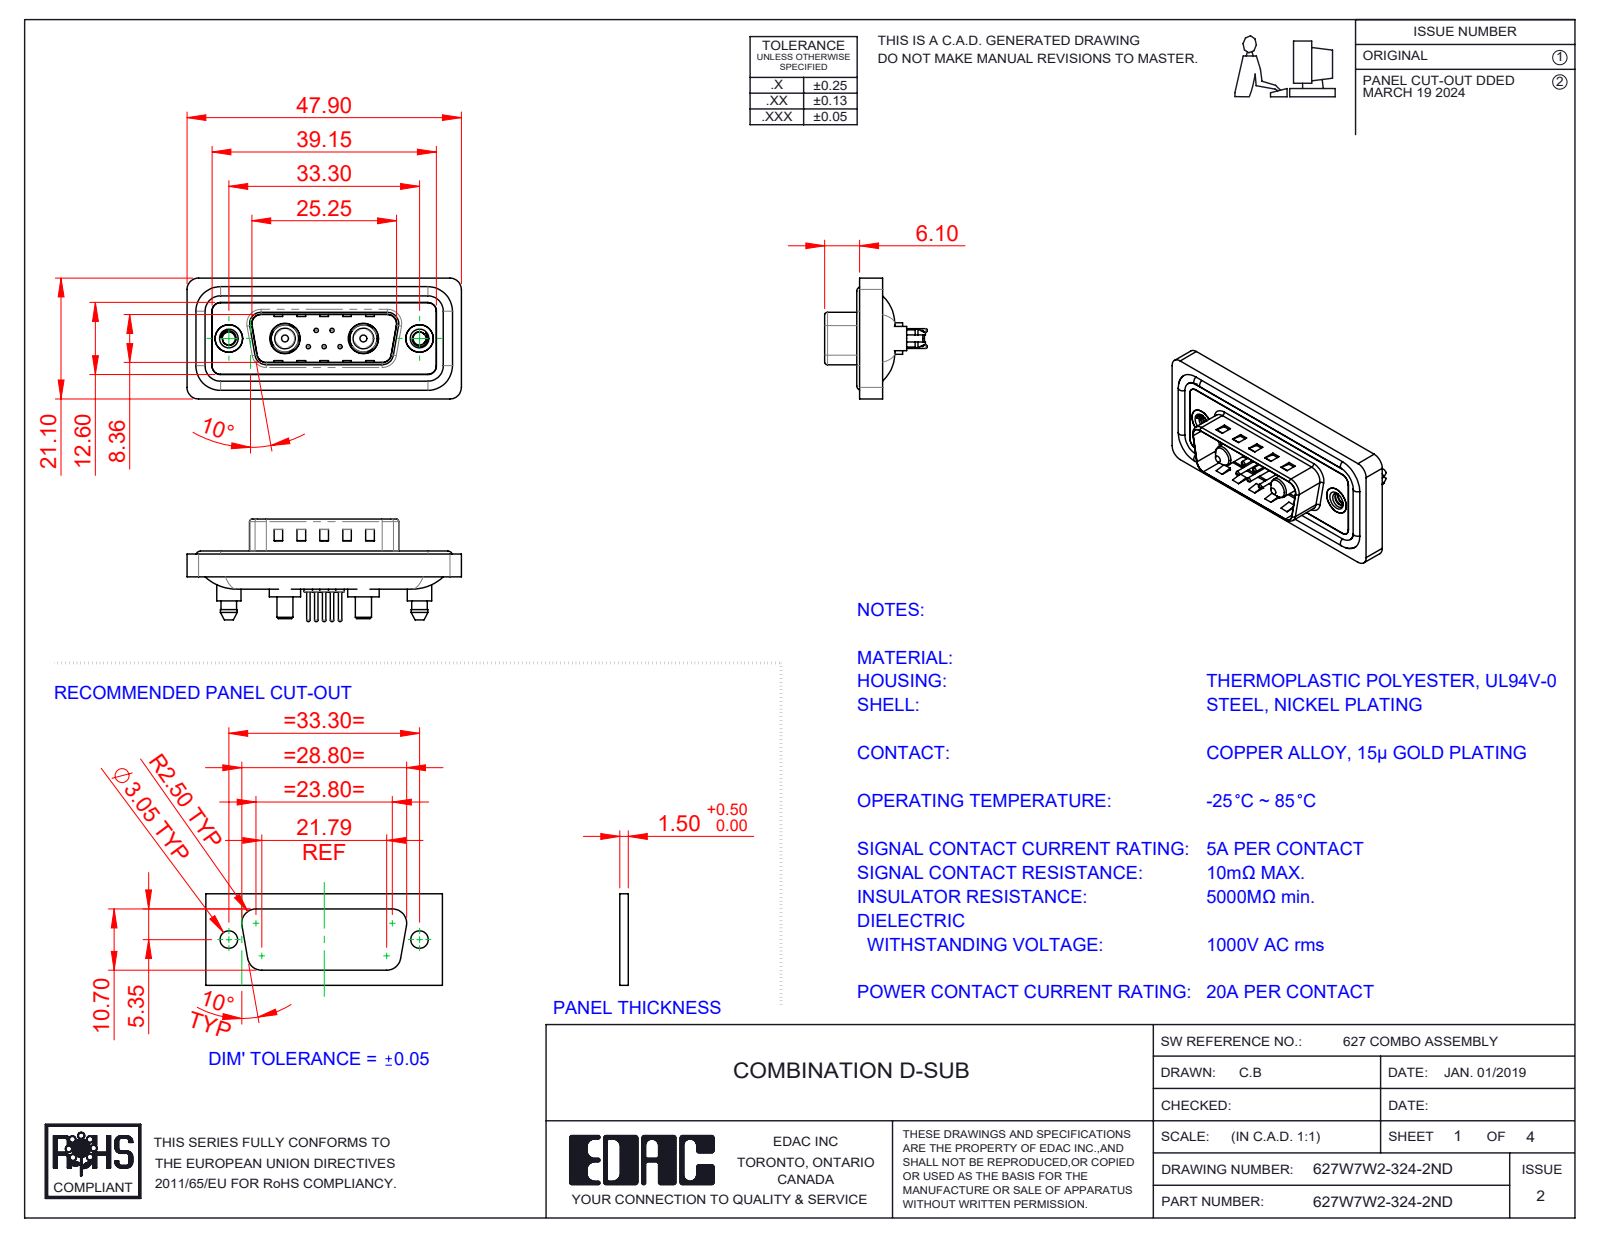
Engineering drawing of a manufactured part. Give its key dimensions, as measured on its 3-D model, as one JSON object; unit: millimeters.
{"part_name": "627Combo Contact Row 2_24; 627Combo Housing_7W2; 627Combo Shell Front_15 Contacts; 627Combo Threaded Boardlock_5 (+6 more)", "step_written_by": "SolidWorks 2023 (CONFIG_CONTROL_DESIGN)", "units": "millimeters", "bodies": {"solids": 16, "faces": 768, "planar": 248, "cylindrical": 332, "other": 188}, "overall_size": [47.9, 21.1, 17.9], "volume_mm3": 5651, "surface_area_mm2": 9129, "round_holes": [[0.75, 5], [1.6, 5], [2, 5], [2.26, 2], [4, 2], [4.8, 2], [4.85, 2], [5, 2], [5.3, 2]], "round_bosses_or_shafts": [[1.5, 5], [0.6, 5], [1.6, 4], [5.5, 2], [5.4, 2], [5.2, 2], [4.9, 2], [4.75, 2]], "partial_cylinders_radius": [[1.5, 28], [2, 20], [1.6, 10], [0.5, 8], [0.25, 4], [0.6, 4], [0.65, 4], [0.9, 4]], "face_to_face_distances": [0.4, 1.1, 1.5, 1.6, 0.5, 3.1, 2.9, 4, 0.7, 0.82], "hole_center_spacings": [3.16, 2.77, 9.8, 23.5, 4.31, 4.33, 5.03, 5.04]}
